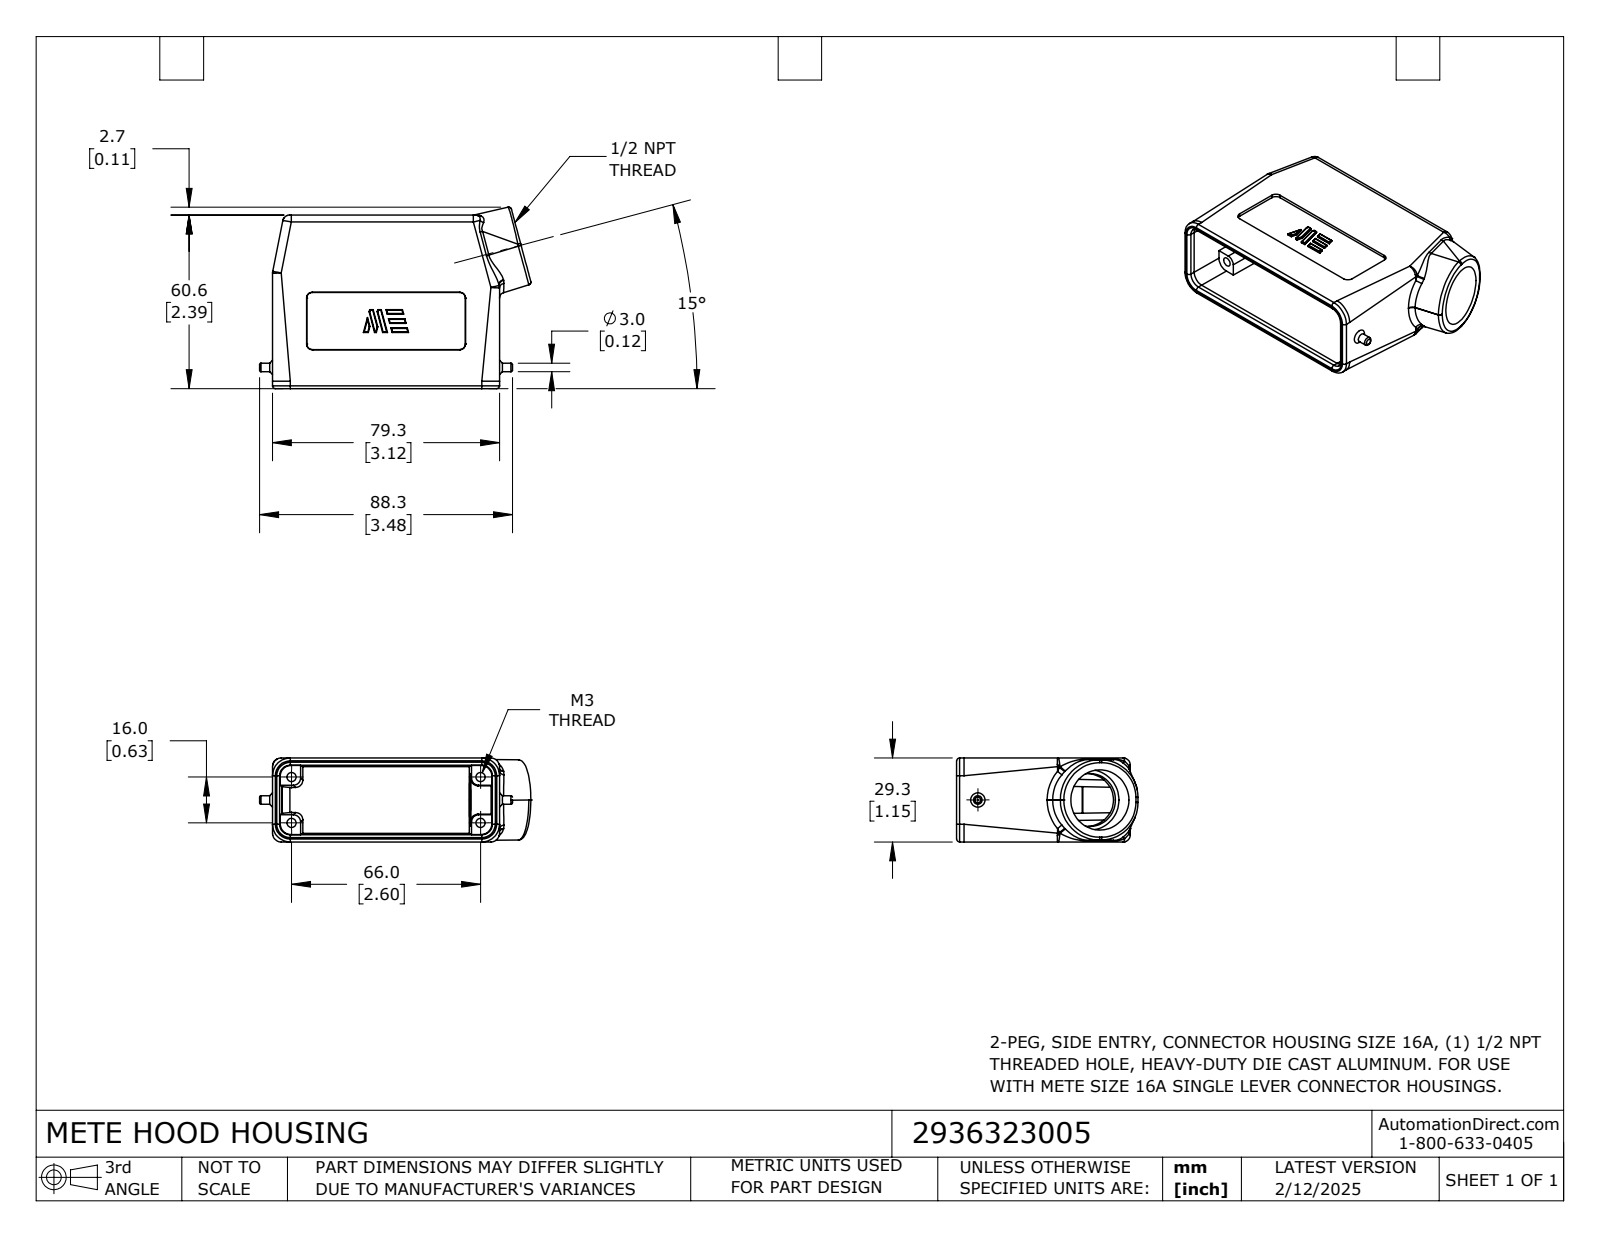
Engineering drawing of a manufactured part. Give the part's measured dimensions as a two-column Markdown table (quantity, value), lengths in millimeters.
| quantity | value |
| --- | --- |
| part name | 2936323005 |
| STEP written by | SolidWorks 2024 (CONFIG_CONTROL_DESIGN) |
| units | millimeters |
| bodies | 1 solid, 302 faces (119 planar, 113 cylindrical, 70 other) |
| overall size | 94.7 × 63.3 × 29.3 |
| volume | 44 150 mm³ |
| surface area | 29 550 mm² |
| round holes (diameter × count) | 3.2 × 4, 18.5 × 1, 21 × 1 |
| round bosses / shafts (diameter × count) | 3 × 1 |
| partial cylindrical surfaces (radius × count) | 0.2 × 38, 1 × 13, 2 × 4, 2.4 × 4, 2.5 × 4, 3 × 4, 3.7 × 4, 6.2 × 4 |
| main face-to-face distances | 29.3, 28.3, 1, 2.5, 27.3, 7.1, 79.3, 26.8, 1.5, 25.8 |
| hole center spacings | 16, 66, 67.9 |
